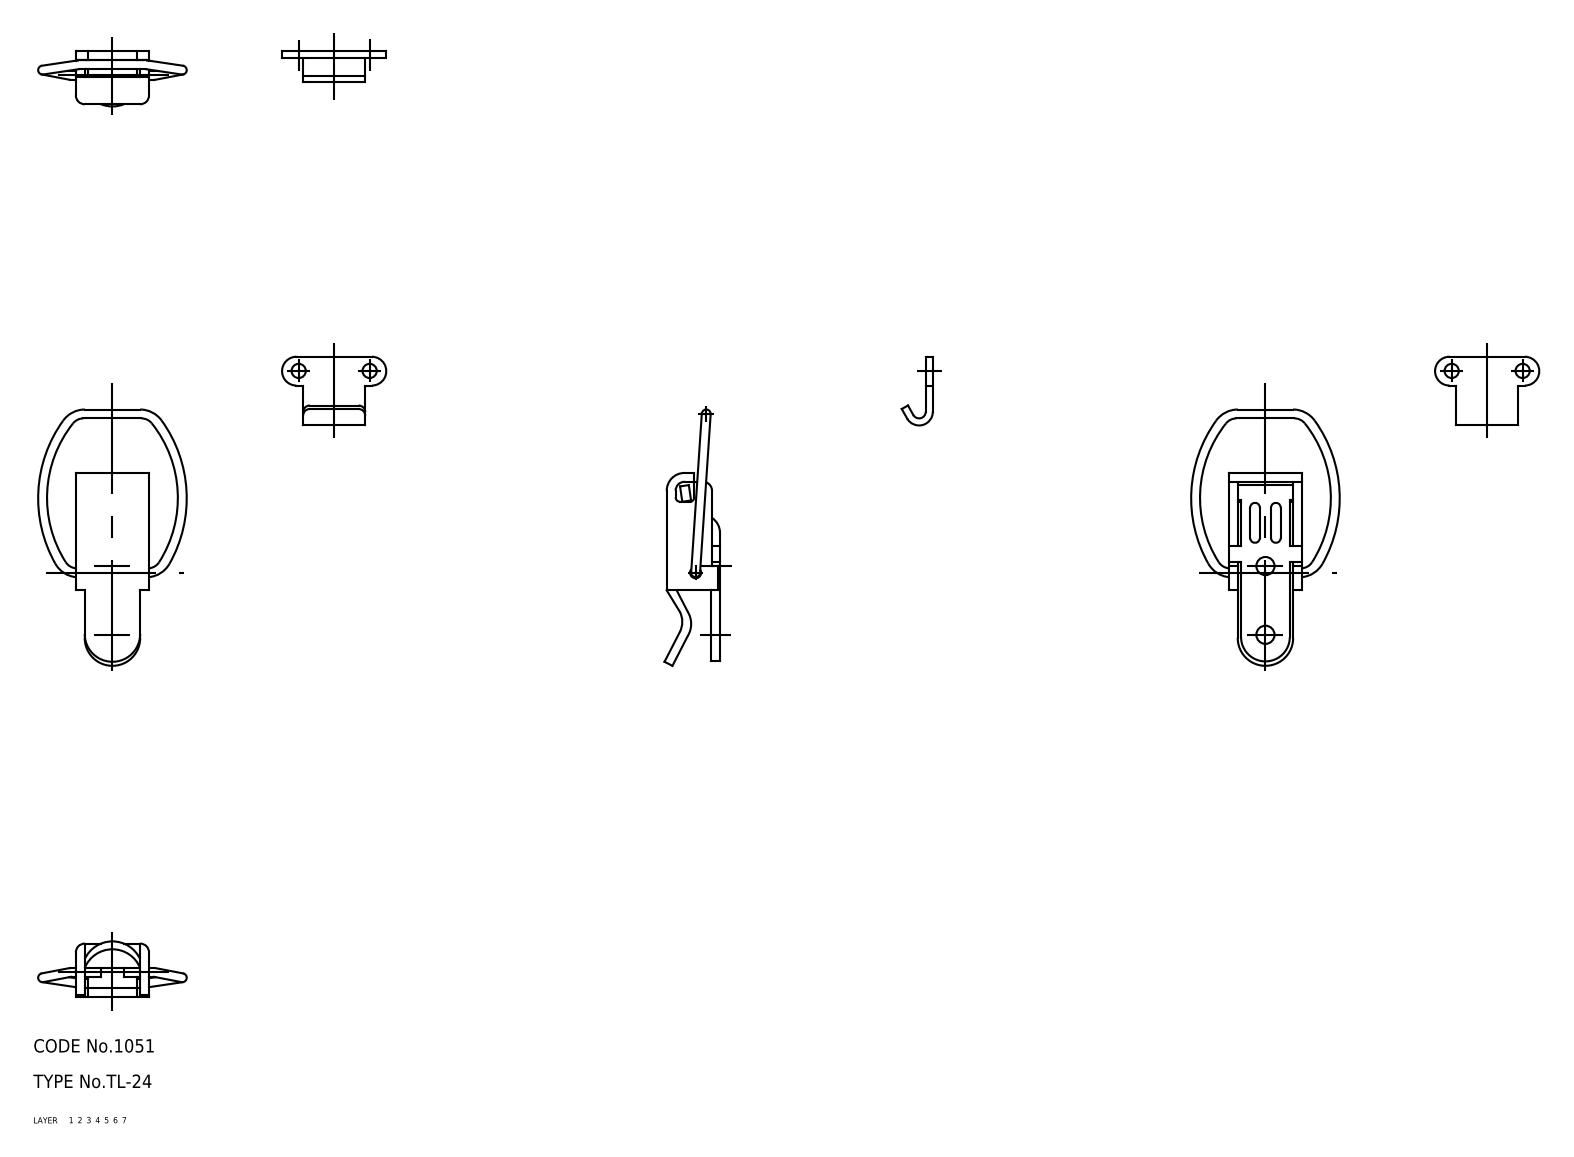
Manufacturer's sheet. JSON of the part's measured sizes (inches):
{"part_name": "lever; keeper; base; arm (+1 more)", "step_written_by": "CADfix (AUTOMOTIVE_DESIGN)", "units": "inches", "bodies": {"solids": 4, "faces": 202, "planar": 0, "cylindrical": 0, "other": 202}, "overall_size": [2.744, 1.319, 0.492], "volume_in3": 0.237, "surface_area_in2": 8.124}
